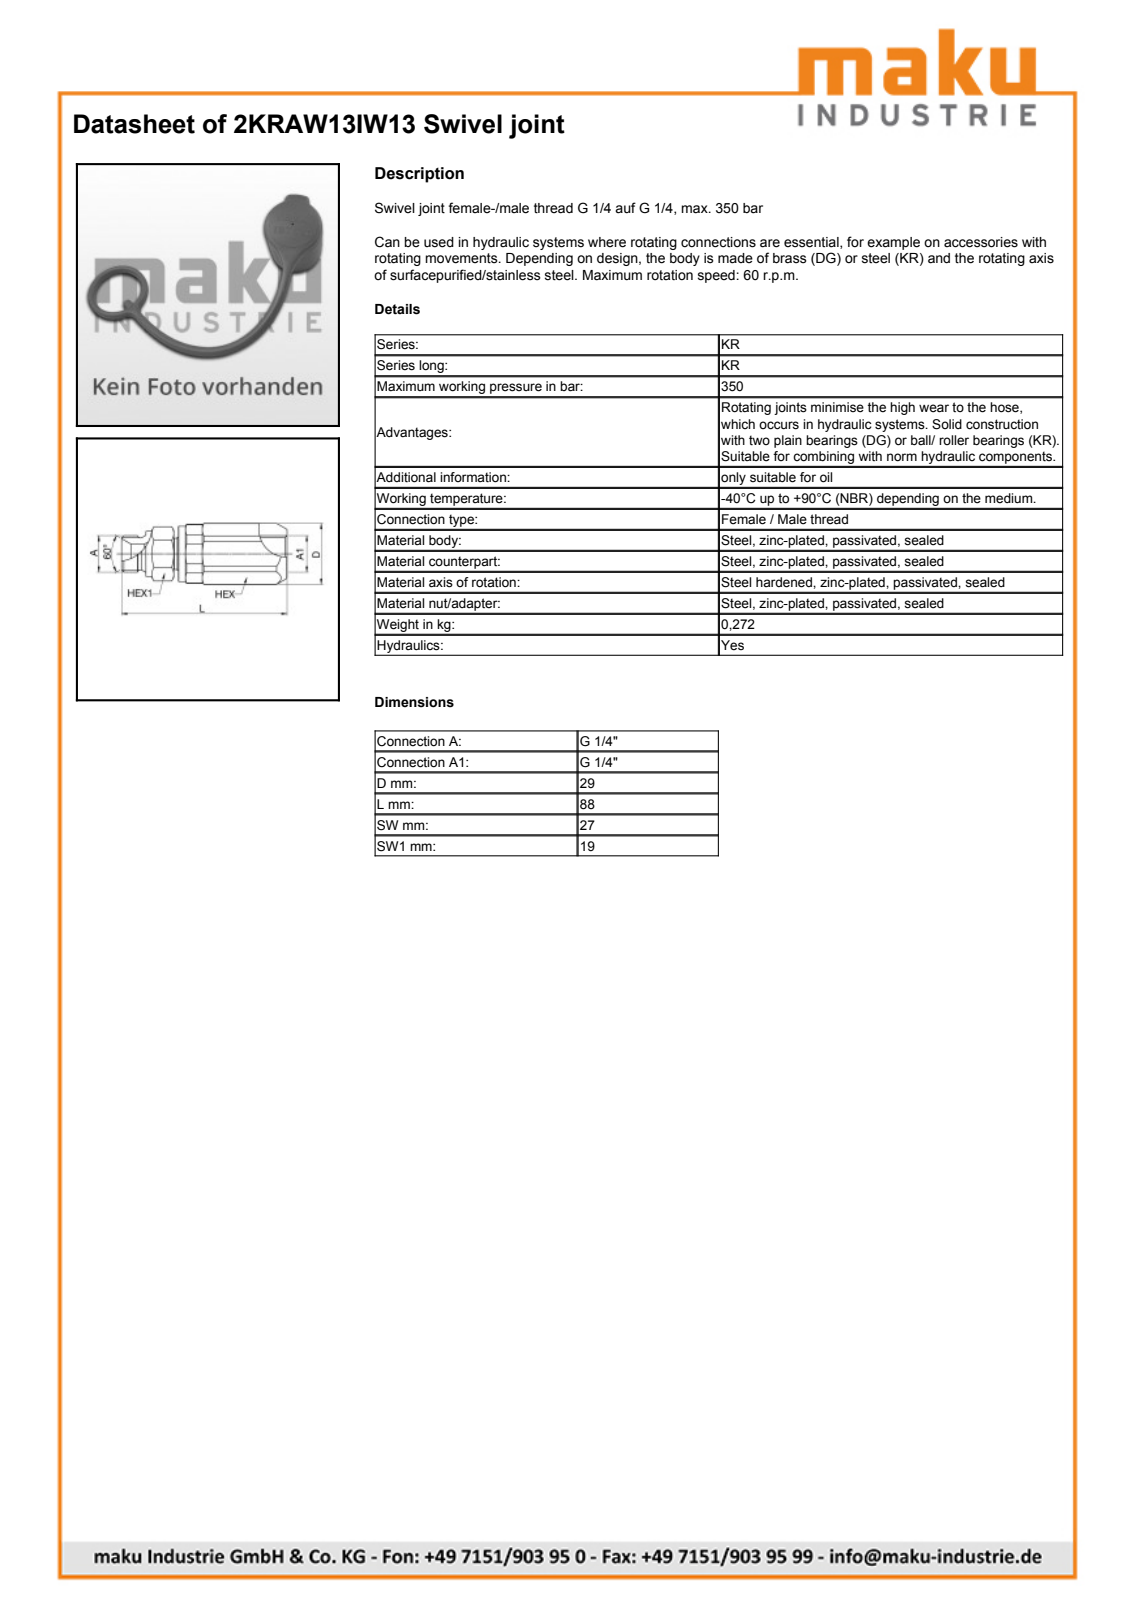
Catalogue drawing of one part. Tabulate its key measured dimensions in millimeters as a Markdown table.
| quantity | value |
| --- | --- |
| part name | 2KRAW13IW13 |
| STEP written by | SolidWorks 2009 (AUTOMOTIVE_DESIGN) |
| units | millimeters |
| bodies | 1 solid, 150 faces (38 planar, 42 cylindrical, 70 other) |
| overall size | 87.5 × 29 × 27 |
| volume | 36 841 mm³ |
| surface area | 10 654 mm² |
| round holes (diameter × count) | 6 × 1, 9.8 × 1, 10.2 × 1, 11.5 × 1, 16 × 1, 24.2 × 1 |
| round bosses / shafts (diameter × count) | 26.7 × 1, 24 × 1, 18 × 1, 13.16 × 1, 11.9 × 1, 11.4 × 1, 10 × 1 |
| partial cylindrical surfaces (radius × count) | 14.5 × 1 |
| main face-to-face distances | 27, 23, 4, 19, 56.3, 58.5, 2.2, 42.7, 13.6, 15.8 |
